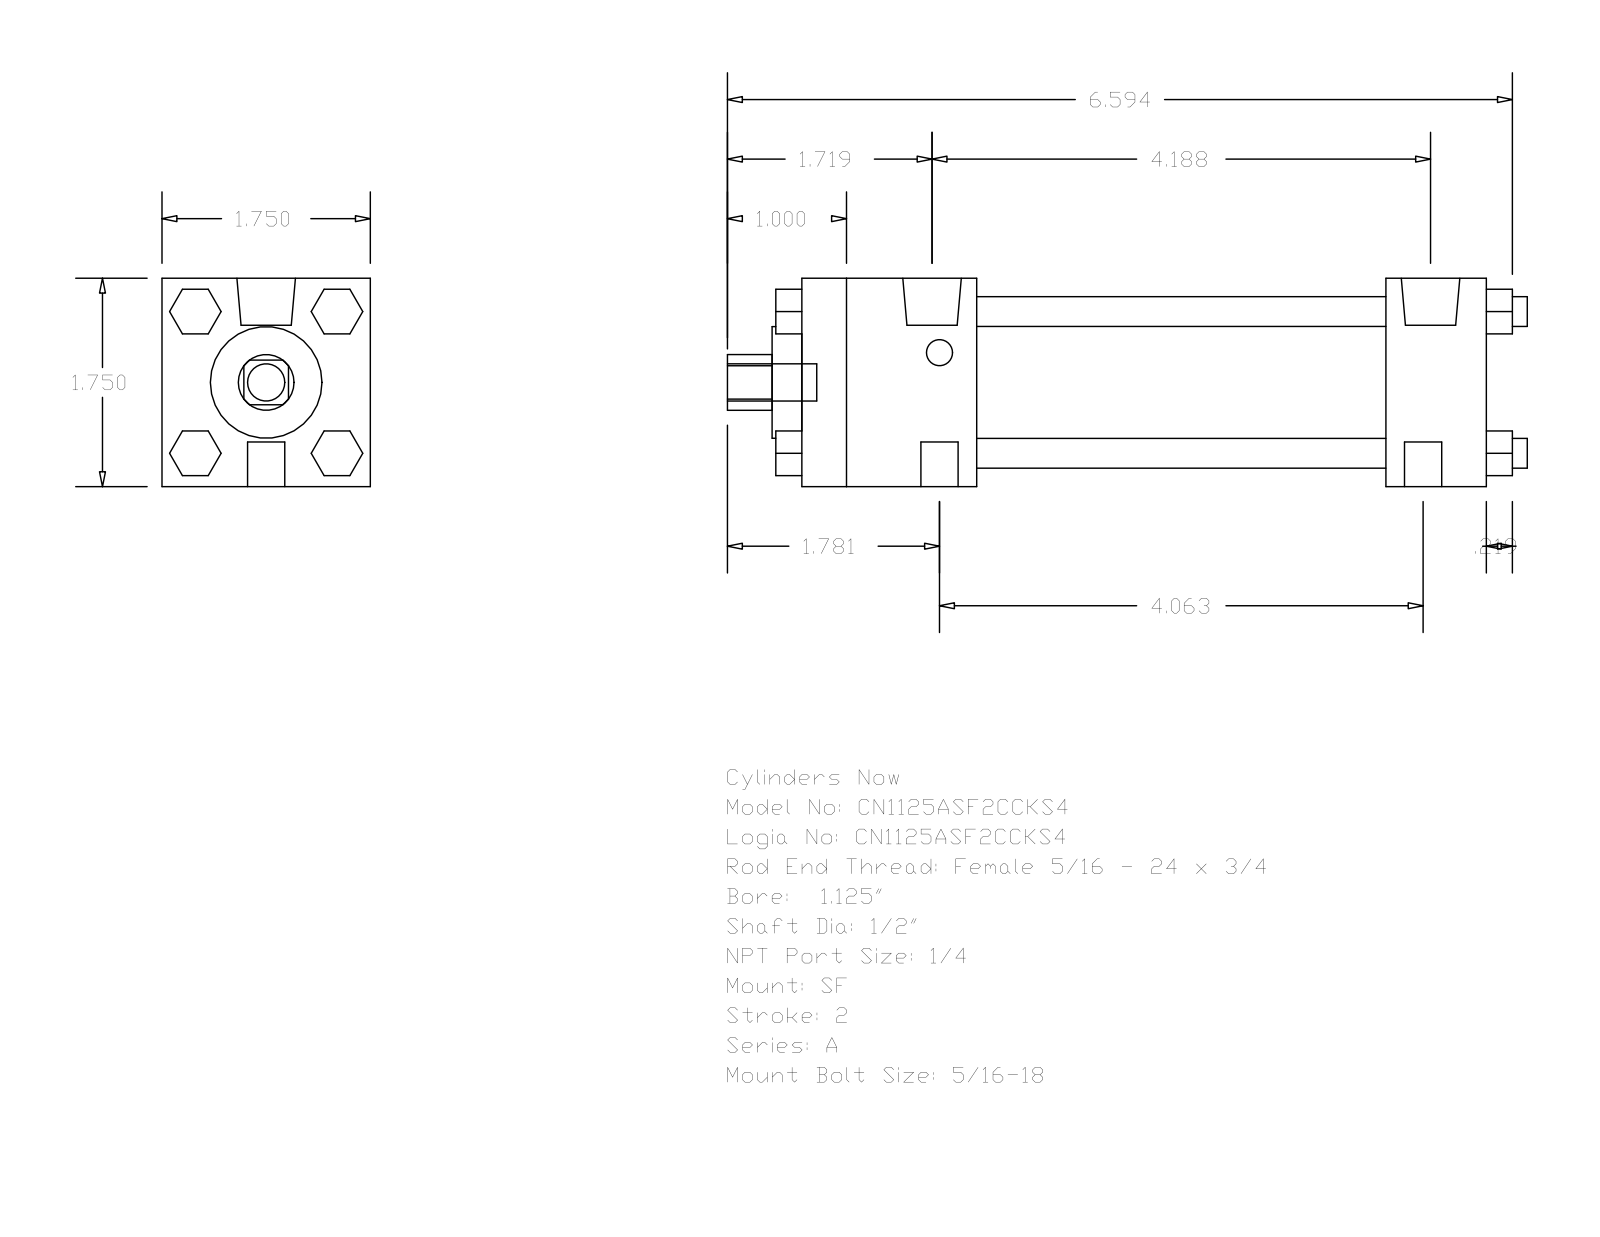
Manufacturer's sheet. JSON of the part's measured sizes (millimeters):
{"part_name": "A_SF__0112_0.5", "step_written_by": "GSSL Pune (CONFIG_CONTROL_DESIGN)", "units": "millimeters", "bodies": {"solids": 0, "faces": 120, "planar": 92, "cylindrical": 28, "other": 0}, "overall_size": [170.66, 44.45, 44.45], "round_holes": [[12.7, 1], [23.81, 1], [31.88, 1]], "round_bosses_or_shafts": [[6.35, 4], [7.94, 3], [12.49, 2], [5.56, 2]], "partial_cylinders_radius": [[5.94, 1]], "face_to_face_distances": [44.46, 146.05, 124.61, 21.44, 37.3, 87.31, 108.75, 9.53, 5.59, 9.52]}
